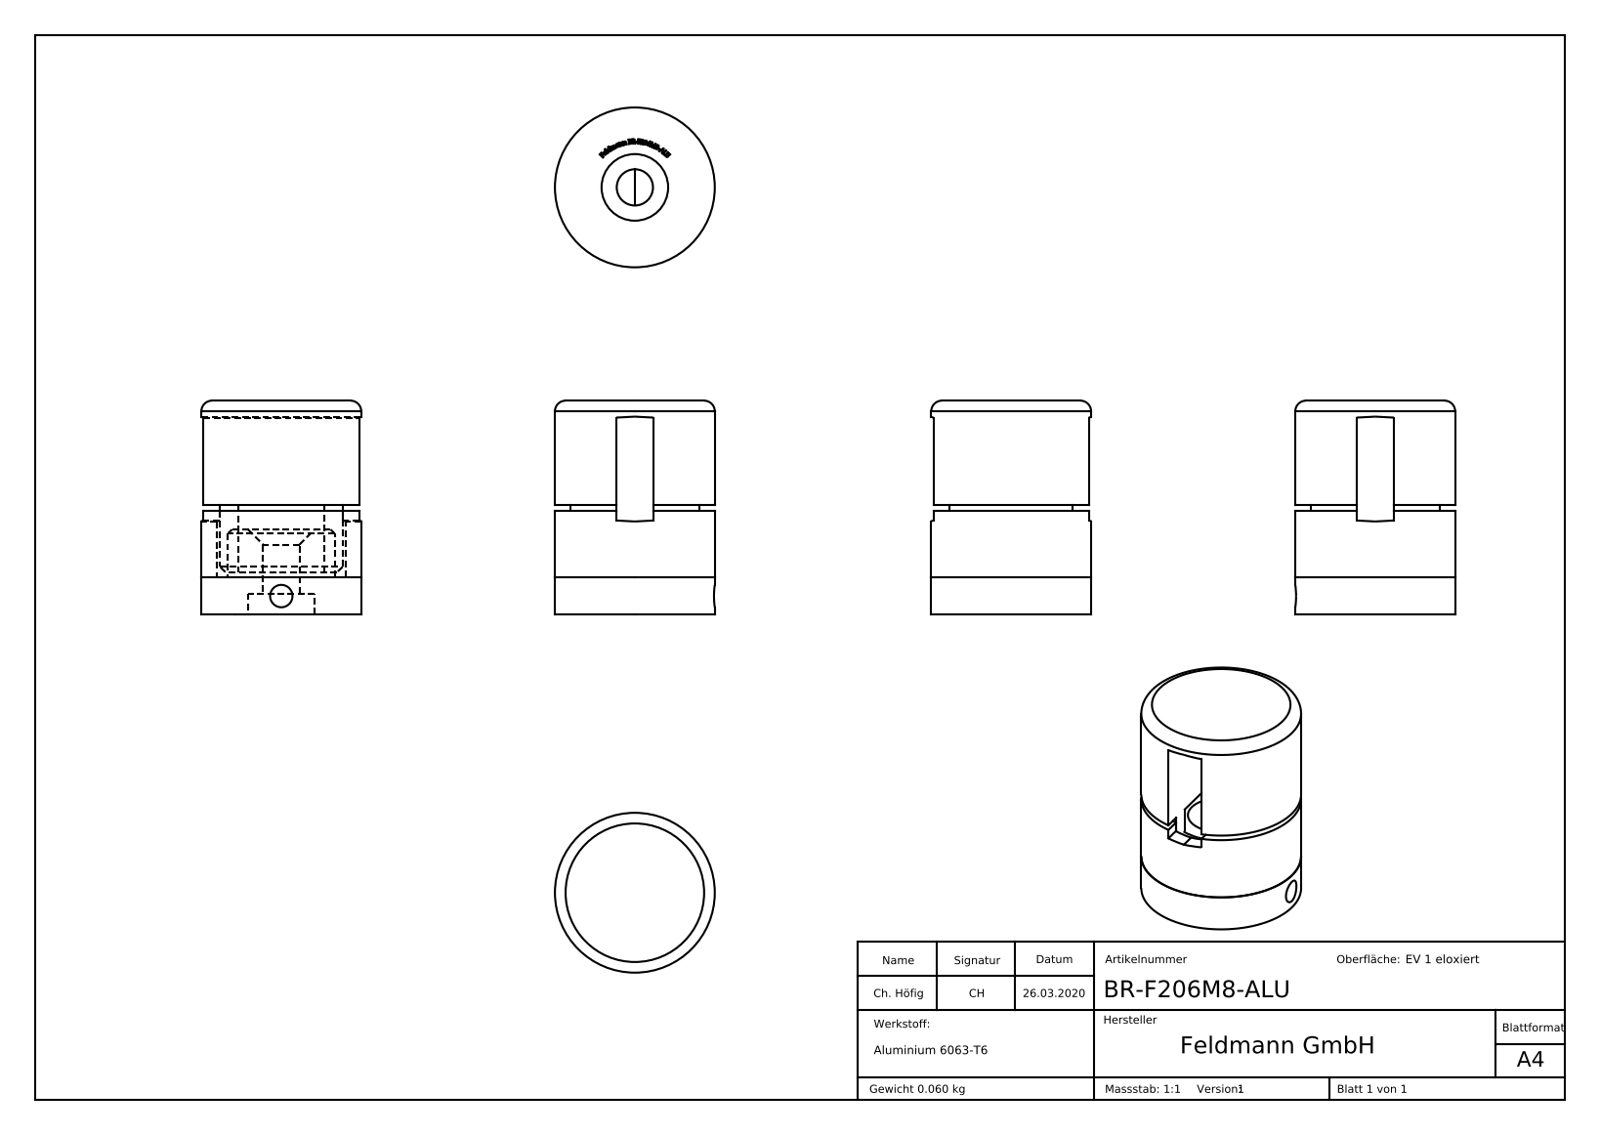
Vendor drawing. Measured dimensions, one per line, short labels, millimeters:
name: BR-F206M8-ALU; BR-R1XM8-XXX Teil1; BR-R1XM8-XXX Teil1_BR-FXXXM8-ALU Teil1; BR-R1XM8-XXX Teil2_BR-F206M8-ALU Teil2 (+3 more)
written by: SolidWorks 2015 (CONFIG_CONTROL_DESIGN)
unit: mm
bodies: 3 solids, 323 faces (196 planar, 12 cylindrical, 115 other)
size: 64.34 × 30 × 30
volume: 22 127 mm³; area: 10 906 mm²
holes: 1× ⌀4.2, 1× ⌀6.8, 1× ⌀12.5, 1× ⌀24.2
bosses: 1× ⌀30, 1× ⌀24.1, 1× ⌀20
rounds: 1× R8.75
face distances: 7, 40.18, 33.18, 20.53, 13.53, 19.65, 1, 12.53, 8, 19.53
